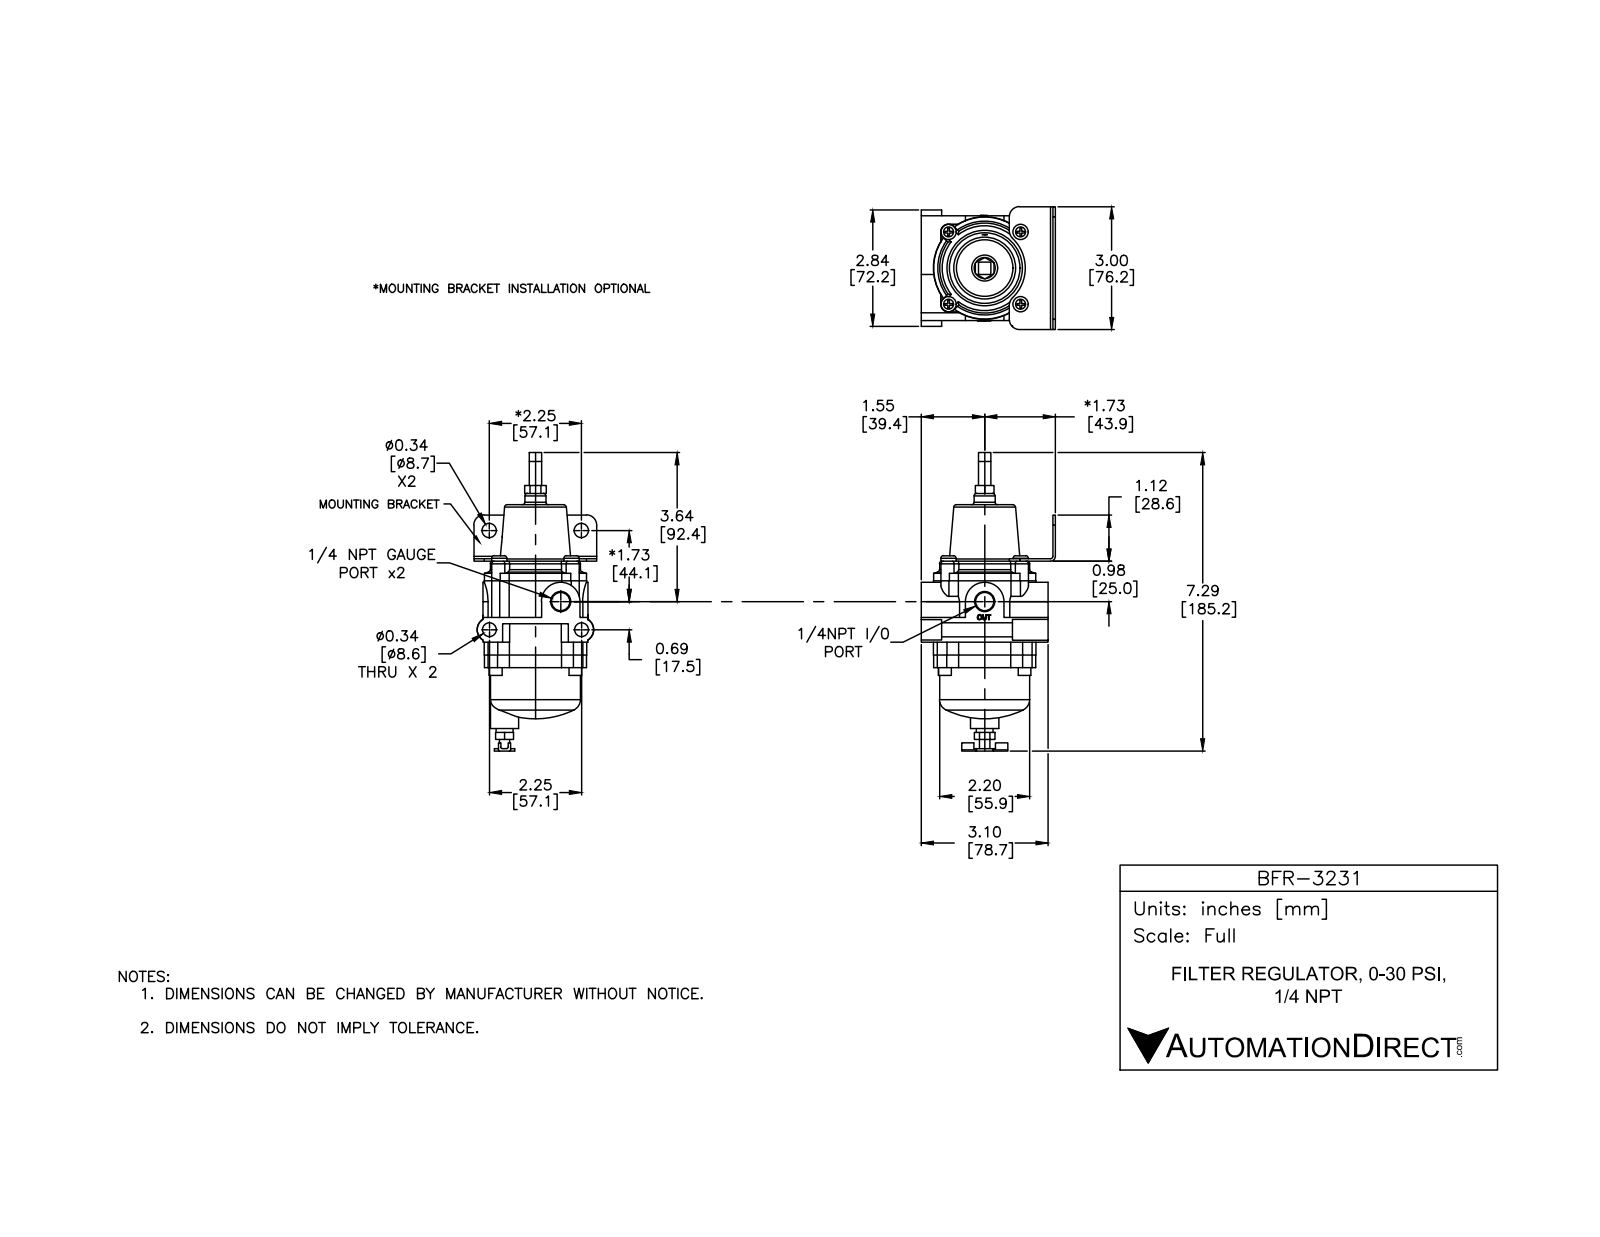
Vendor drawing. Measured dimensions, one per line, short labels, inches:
name: BFR-3231
written by: SolidWorks 2015 (CONFIG_CONTROL_DESIGN)
unit: in
bodies: 15 solids, 1546 faces (316 planar, 994 cylindrical, 236 other)
size: 7.318 × 3.1 × 2.85
volume: 21.53 in³; area: 105.9 in²
holes: 8× ⌀0.159, 8× ⌀0.201, 2× ⌀0.34, 2× ⌀0.438, 1× ⌀0.125, 1× ⌀0.257, 1× ⌀0.26, 1× ⌀0.332
bosses: 8× ⌀0.19, 8× ⌀0.149, 5× ⌀0.312, 4× ⌀0.373, 1× ⌀2.2, 1× ⌀0.688, 1× ⌀0.512, 1× ⌀0.416
rounds: 48× R0.004, 8× R0.1, 8× R0.187, 8× R0.188, 6× R0.02, 4× R0.062, 3× R0.063, 2× R0.039
face distances: 1.81, 0.915, 0.895, 0.31, 1.225, 2.12, 0.6, 0.625, 0.315, 1.495
hole spacings: 1.858, 0.125, 1.944, 1.375, 0.996, 1.25, 1.25, 1.768
